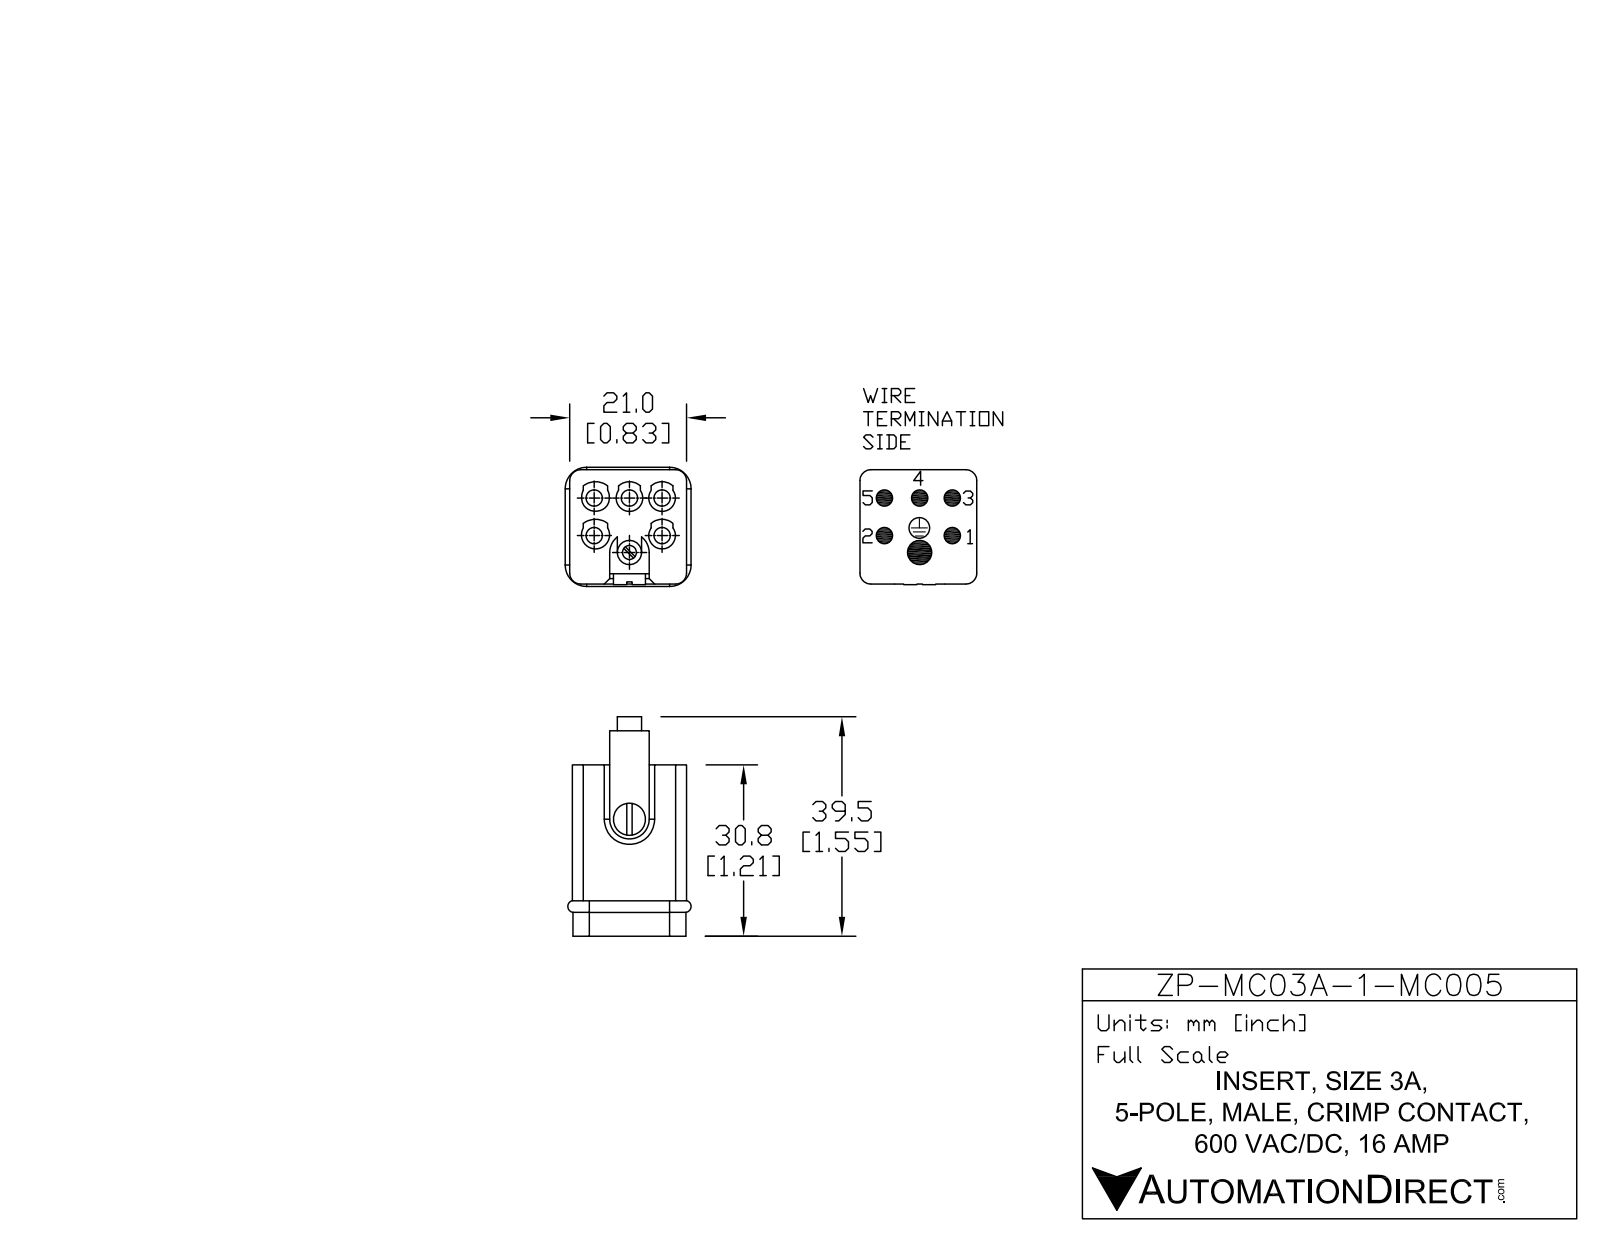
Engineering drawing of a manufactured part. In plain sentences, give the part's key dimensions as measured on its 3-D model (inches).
The part is named "ZP-3A-5-MC-INSERT". Its 3-D file was written by "SolidWorks 2011 (AUTOMOTIVE_DESIGN)". It is 1 solid with 112 faces: 62 planar, 41 cylindrical and 9 other. Overall it measures 1.579 by 0.892 by 0.862 inches. Its volume is 0.515 cubic inches and its surface area 10.1 square inches. Round holes: 5 of diameter 0.118. Round bosses or shafts: 4 of diameter 0.087, 1 of diameter 0.232, 1 of diameter 0.175, 1 of diameter 0.098. Partial cylindrical surfaces (rounded edges, fillets, slot ends): 5 of radius 0.096, 5 of radius 0.119, 4 of radius 0.022, 4 of radius 0.059, 4 of radius 0.079, 4 of radius 0.118, 2 of radius 0.143. The main face-to-face distances are 0.827, 0.116, 0.711, 0.037, 0.101, 0.726, 0.728, 0.079, 0.256, 0.064. The hole center spacings are 0.236, 0.272, 0.36, 0.472, 0.545.
